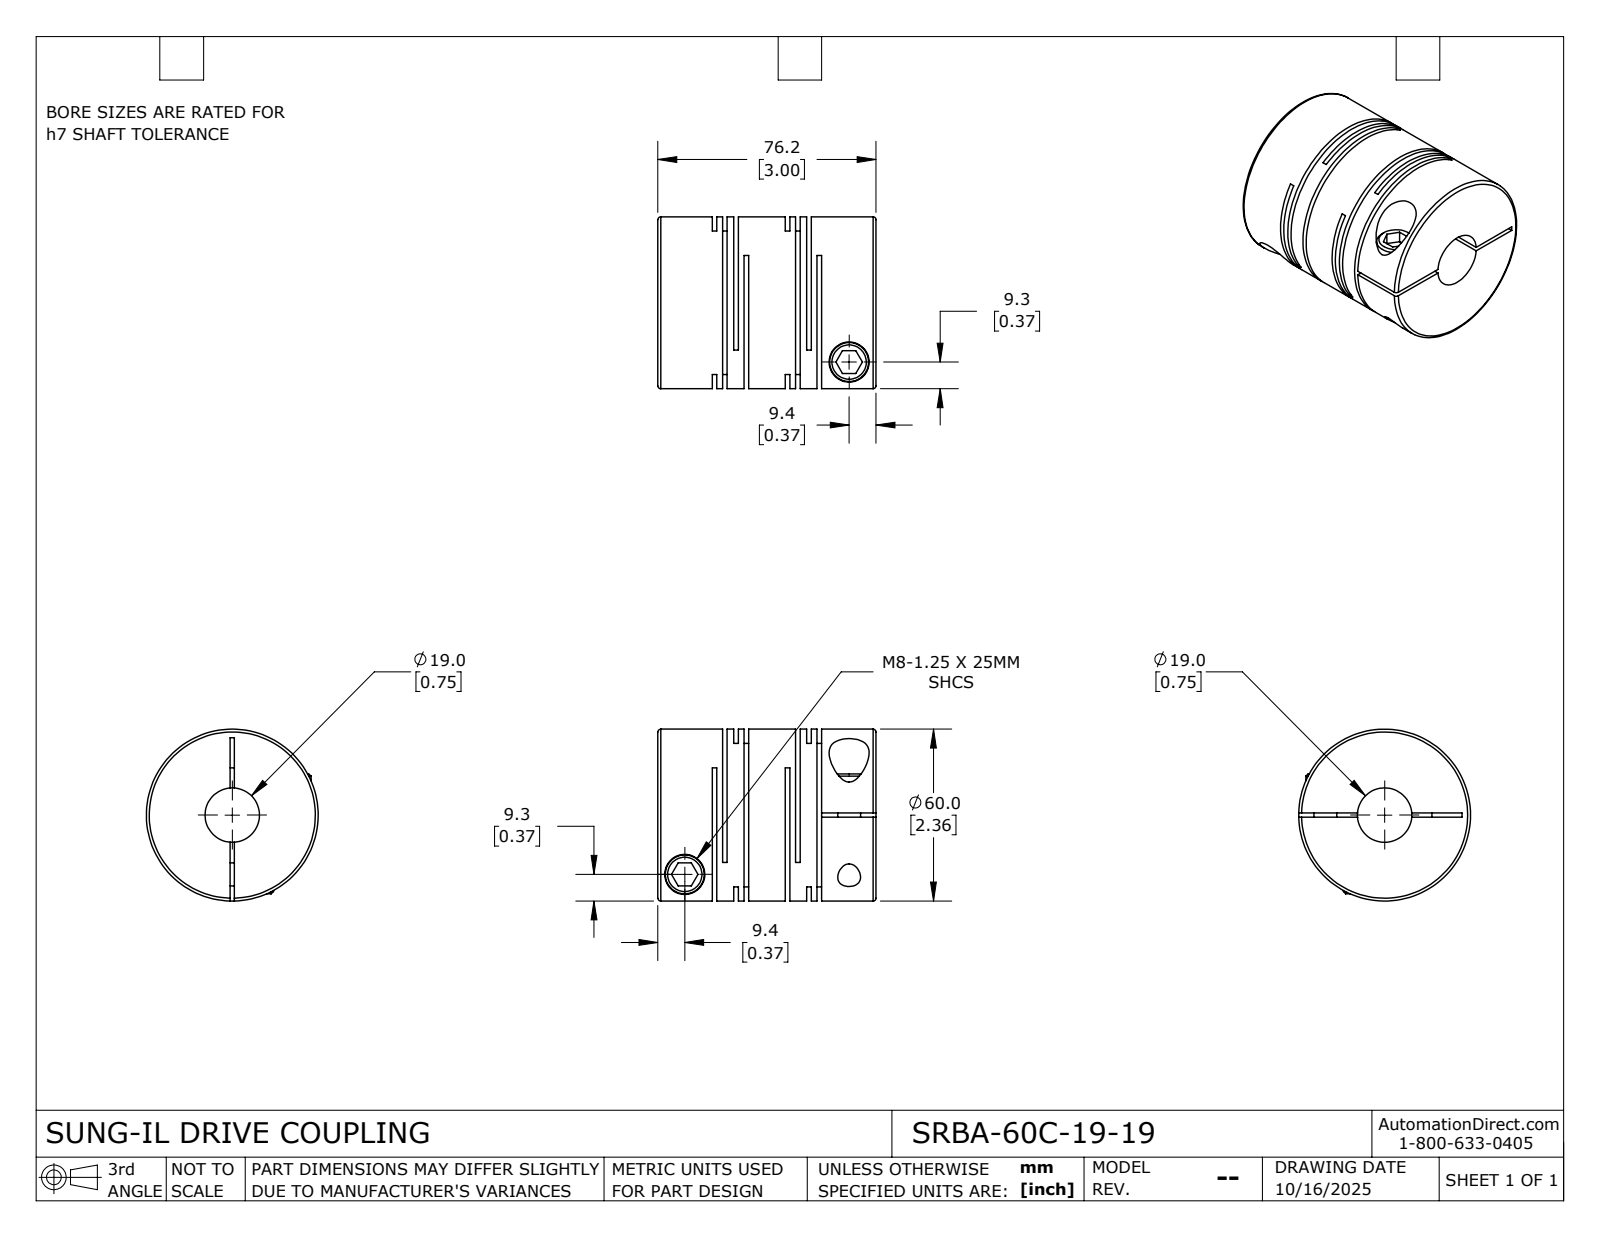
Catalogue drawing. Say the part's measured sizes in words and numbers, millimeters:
The part is named "SRBA-60C-19-19". Its 3-D file was written by "SolidWorks 2024 (CONFIG_CONTROL_DESIGN)". It is 1 solid with 115 faces: 60 planar, 42 cylindrical and 13 other. Overall it measures 76.2 by 60 by 60 millimeters. Its volume is 162 163 cubic millimeters and its surface area 59 544 square millimeters. Round holes: 2 of diameter 8, 2 of diameter 14, 1 of diameter 19. Round bosses or shafts: 2 of diameter 13.6, 1 of diameter 60. The main face-to-face distances are 1.6, 7.5, 25.5, 3.6, 33, 2, 5.9, 3.9, 23.9, 21.9.
